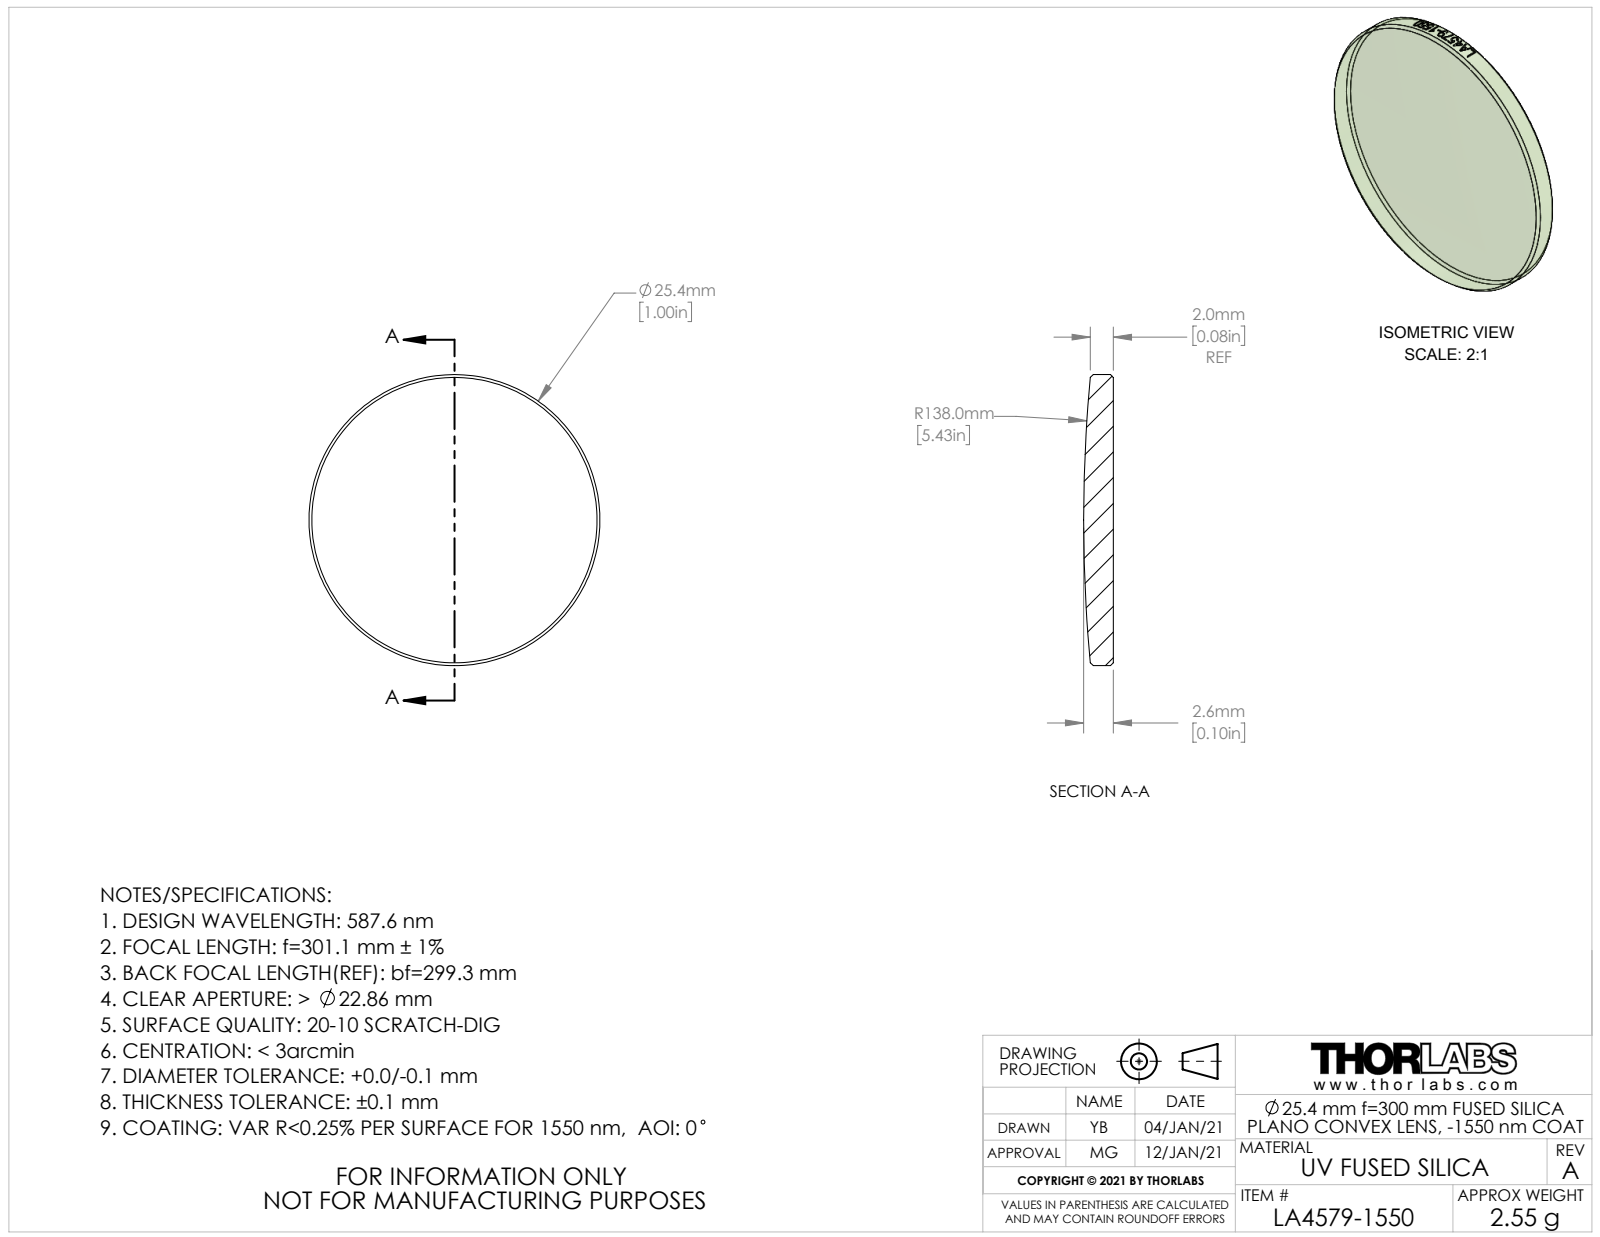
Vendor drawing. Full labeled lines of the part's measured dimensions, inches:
Part name (STEP PRODUCT): CTN015948-E0W
STEP written by: SolidWorks 2018 (AUTOMOTIVE_DESIGN)
Units: inches
Bodies: 1 solid, 27 faces (1 planar, 20 cylindrical, 6 other)
Overall size (bounding box): 1 × 1 × 0.102
Volume: 0.071 in³ · Surface area: 1.785 in²
Round bosses / shafts (diameter × count): ⌀1 ×1
